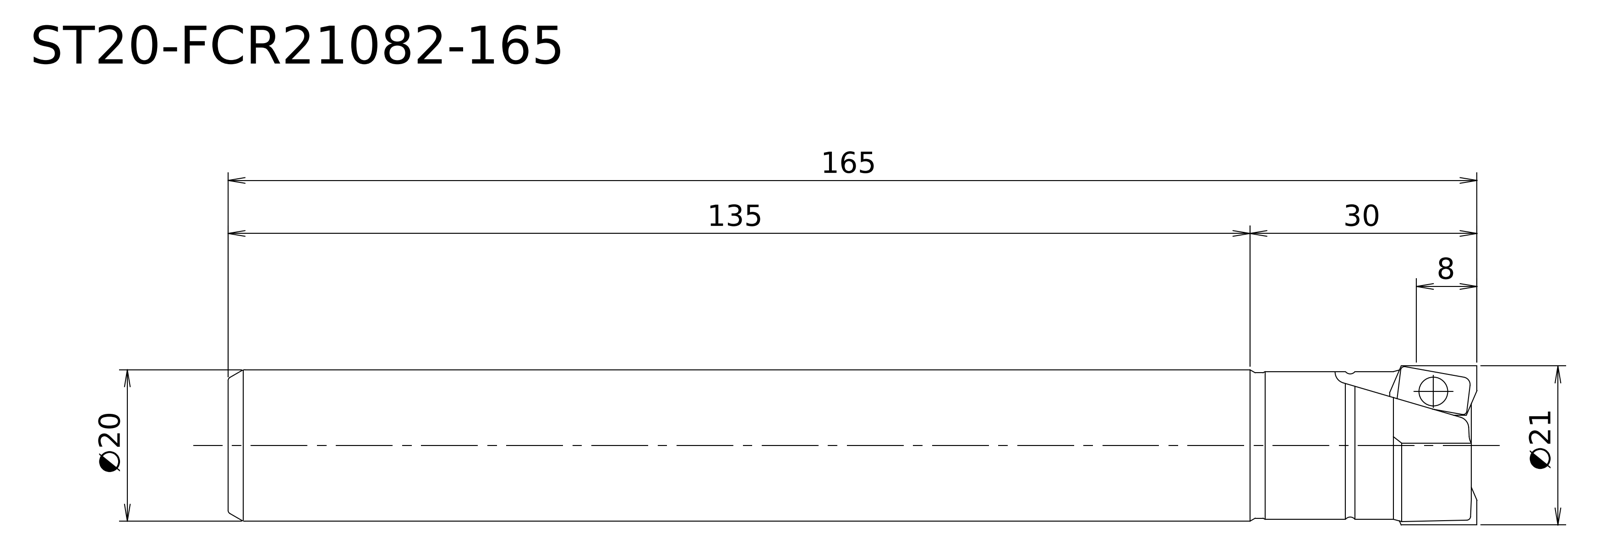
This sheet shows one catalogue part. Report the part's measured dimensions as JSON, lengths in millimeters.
{"step_written_by": "Kubotek KeyCreator V8.5.1 (14335) (CONFIG_CONTROL_DESIGN)", "units": "millimeters", "bodies": {"solids": 1, "faces": 7, "planar": 2, "cylindrical": 3, "other": 2}, "overall_size": [165, 21, 21], "volume_mm3": 51860, "surface_area_mm2": 11064, "round_bosses_or_shafts": [[21, 1], [20, 1], [19.5, 1]], "face_to_face_distances": [165]}
